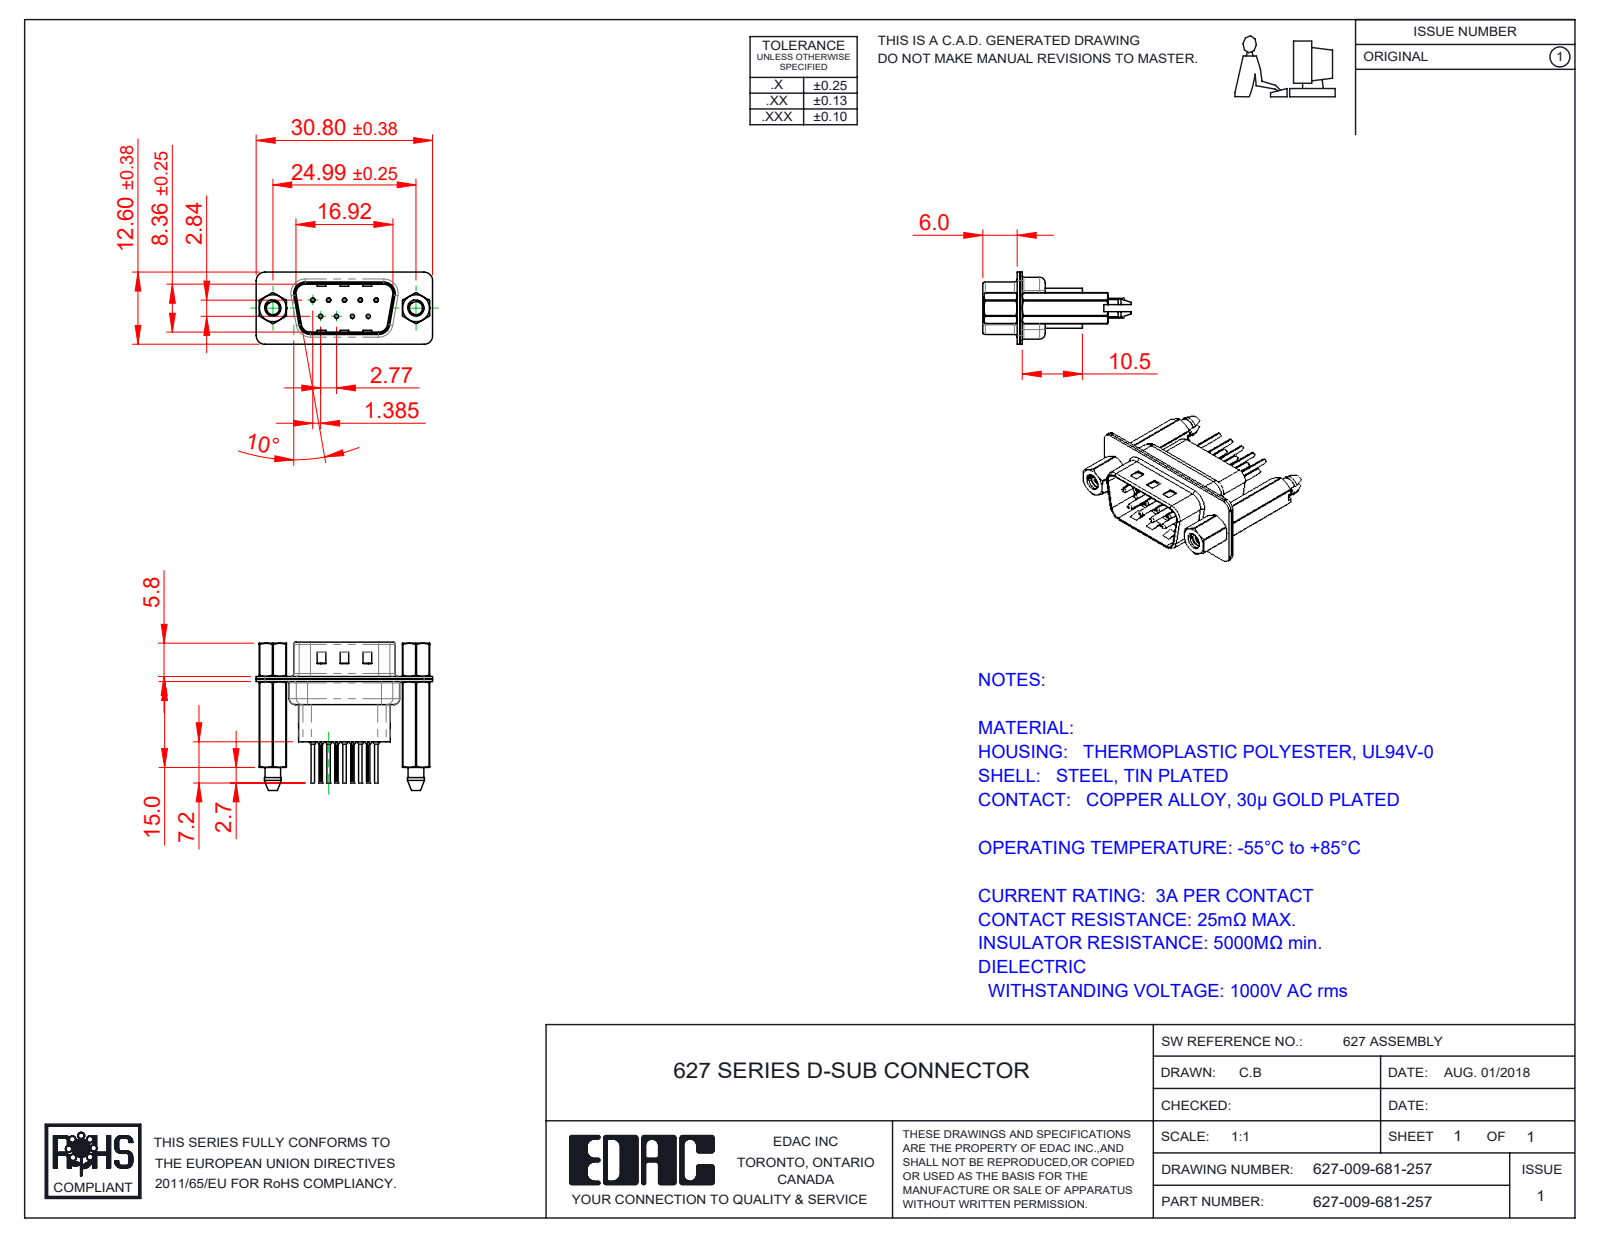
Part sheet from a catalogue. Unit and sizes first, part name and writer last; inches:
Units: inches
Overall size (bounding box): 1.213 × 1.02 × 0.496
Round holes (diameter × count): ⌀0.008 ×9, ⌀0.014 ×9, ⌀0.043 ×9, ⌀0.063 ×9, ⌀0.089 ×2, ⌀0.09 ×2, ⌀0.157 ×2, ⌀0.189 ×2
Round bosses / shafts (diameter × count): ⌀0.079 ×9, ⌀0.059 ×9, ⌀0.03 ×9, ⌀0.024 ×9, ⌀0.193 ×2, ⌀0.11 ×2
Partial cylindrical surfaces — rounded edges, fillets, slot ends (radius × count): R0.059 ×20, R0.004 ×18, R0.079 ×12, R0.063 ×10, R0.02 ×8, R0.01 ×4, R0.024 ×4, R0.026 ×4
Main face-to-face distances: 0.018, 0.016, 0.035, 0.187, 0.032, 0.377, 0.055, 0.059, 0.027, 0.302
Hole centre spacings: 0.124, 0.109, 0.218, 0.198, 0.198, 0.327, 0.294, 0.295
Volume: 0.145 in³ · Surface area: 9.393 in²
Bodies: 16 solids, 1420 faces (377 planar, 600 cylindrical, 443 other)
Part name (STEP PRODUCT): 627 Shell Front_09 Contacts; 627 Contact Row 2_61; 627 Housing_09 HP; 627-009-681-257 (+4 more)
STEP written by: SolidWorks 2020 (CONFIG_CONTROL_DESIGN)
